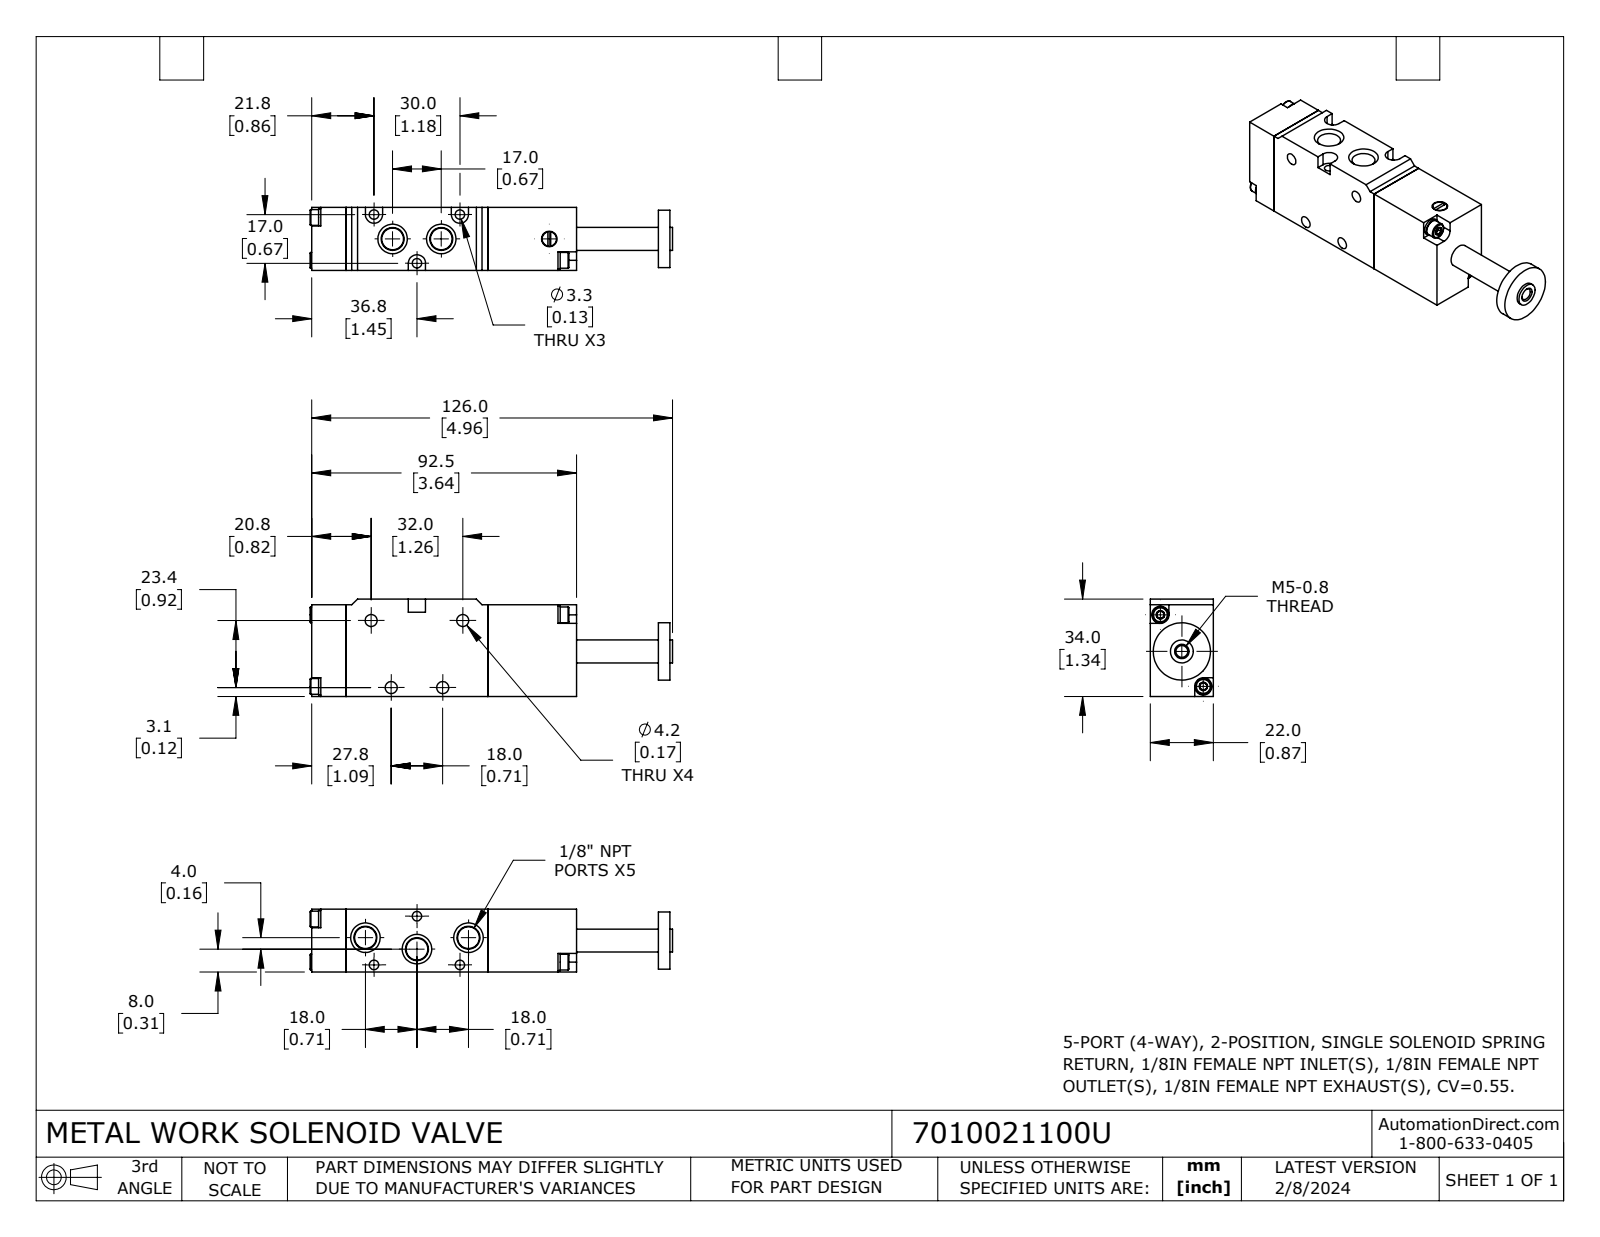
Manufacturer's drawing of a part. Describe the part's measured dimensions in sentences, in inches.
The part is named "7010021100U". Its 3-D file was written by "SolidWorks 2023 (CONFIG_CONTROL_DESIGN)". It is 11 solids with 272 faces: 125 planar, 69 cylindrical and 78 other. Overall it measures 4.984 by 1.339 by 0.866 inches. Its volume is 3.984 cubic inches and its surface area 30.92 square inches. Round holes: 4 of diameter 0.118, 4 of diameter 0.165, 3 of diameter 0.13, 1 of diameter 0.163, 1 of diameter 0.213. Round bosses or shafts: 4 of diameter 0.236, 4 of diameter 0.217, 1 of diameter 0.787, 1 of diameter 0.315, 1 of diameter 0.197. Partial cylindrical surfaces (rounded edges, fillets, slot ends): 3 of radius 0.118. The main face-to-face distances are 0.866, 1.949, 1.26, 1.339, 0.079, 0.472, 2.421, 1.22, 3.642, 3.169. The hole center spacings are 0.564, 0.584, 0.591, 0.893, 0.961, 0.984, 1.148, 1.348.
